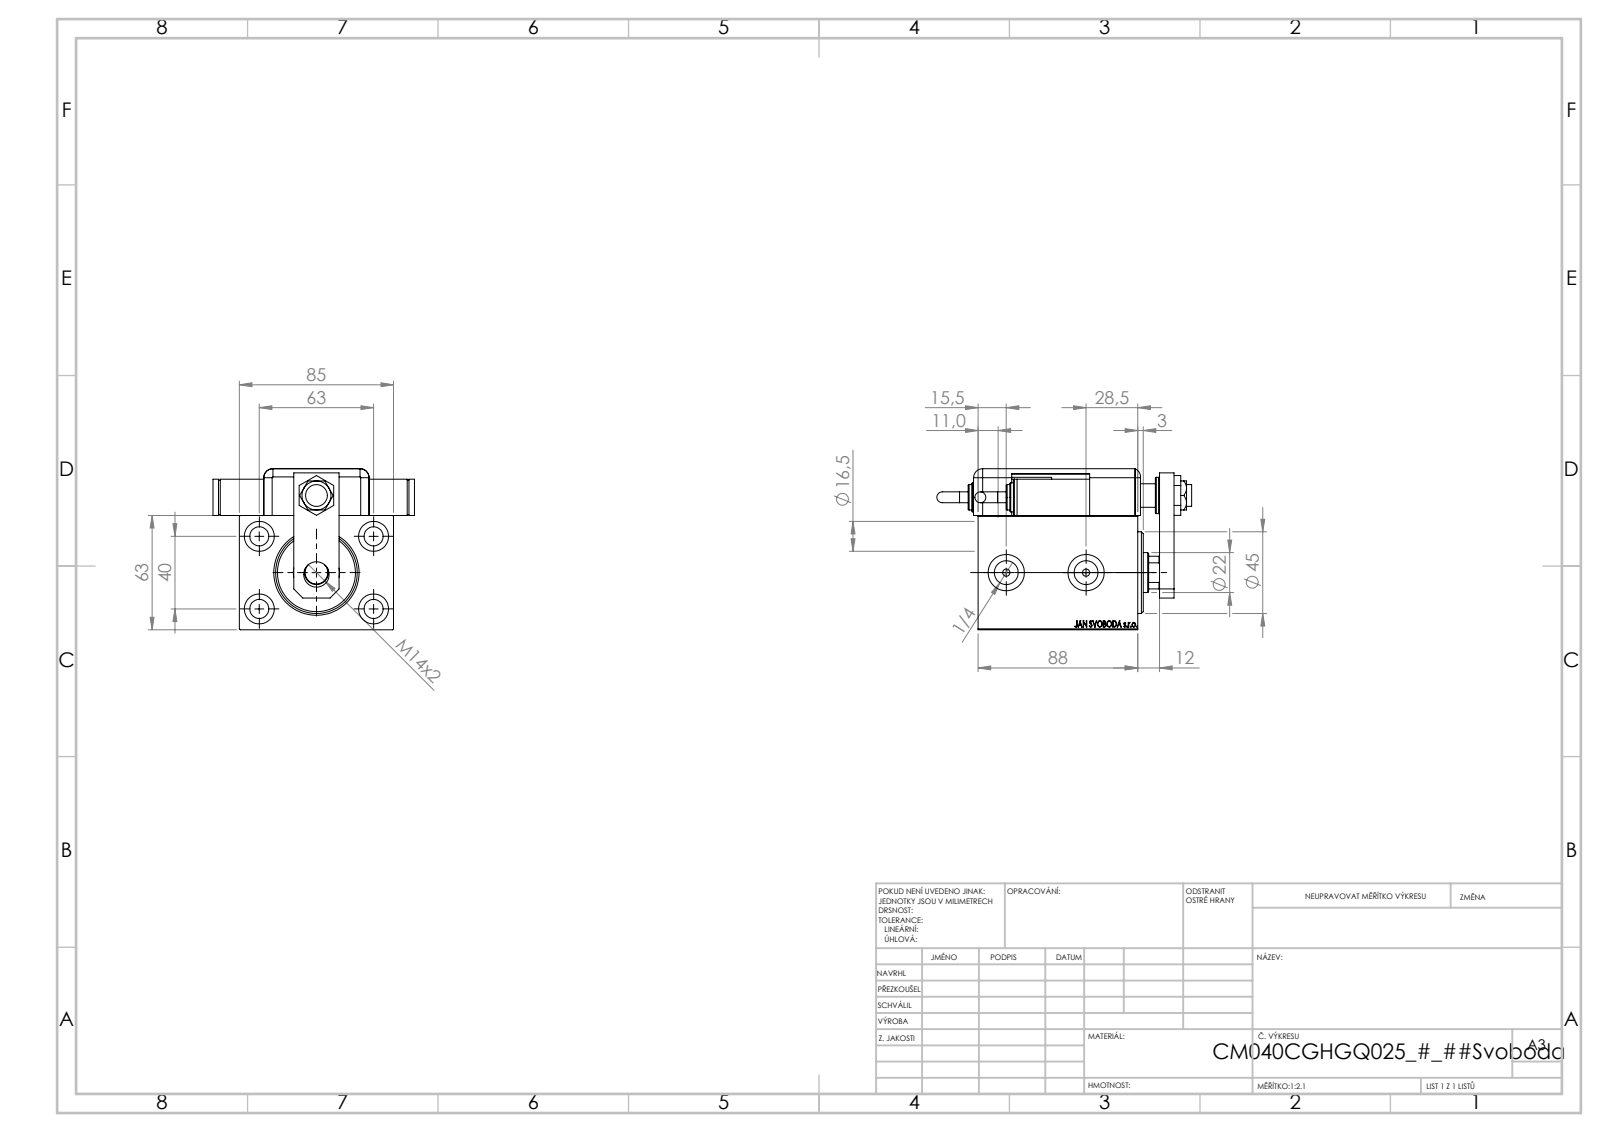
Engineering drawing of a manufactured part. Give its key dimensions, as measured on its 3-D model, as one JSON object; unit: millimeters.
{"part_name": "TYC; ZARAZKA_Q; NUT_D13; SWITCH DIM A_G (+7 more)", "step_written_by": "SolidWorks 2019 (CONFIG_CONTROL_DESIGN)", "units": "millimeters", "bodies": {"solids": 13, "faces": 1246, "planar": 614, "cylindrical": 115, "other": 517}, "overall_size": [140.46, 111, 88.8], "volume_mm3": 542356, "surface_area_mm2": 127781, "round_holes": [[4, 4], [10.5, 4], [16.5, 4], [8, 2], [13.16, 2], [14, 2], [20, 2], [12, 1], [12.5, 1], [13, 1], [22, 1], [25.5, 1]], "round_bosses_or_shafts": [[20, 3], [16, 2], [14, 2], [6, 2]], "partial_cylinders_radius": [[5, 9], [10, 1], [10.5, 1]], "face_to_face_distances": [3, 63, 13.5, 85, 12, 83, 10.5, 20, 88, 1.5], "hole_center_spacings": [37.31, 36.79, 37.86, 38.71, 40, 63, 69.99, 74.63]}
